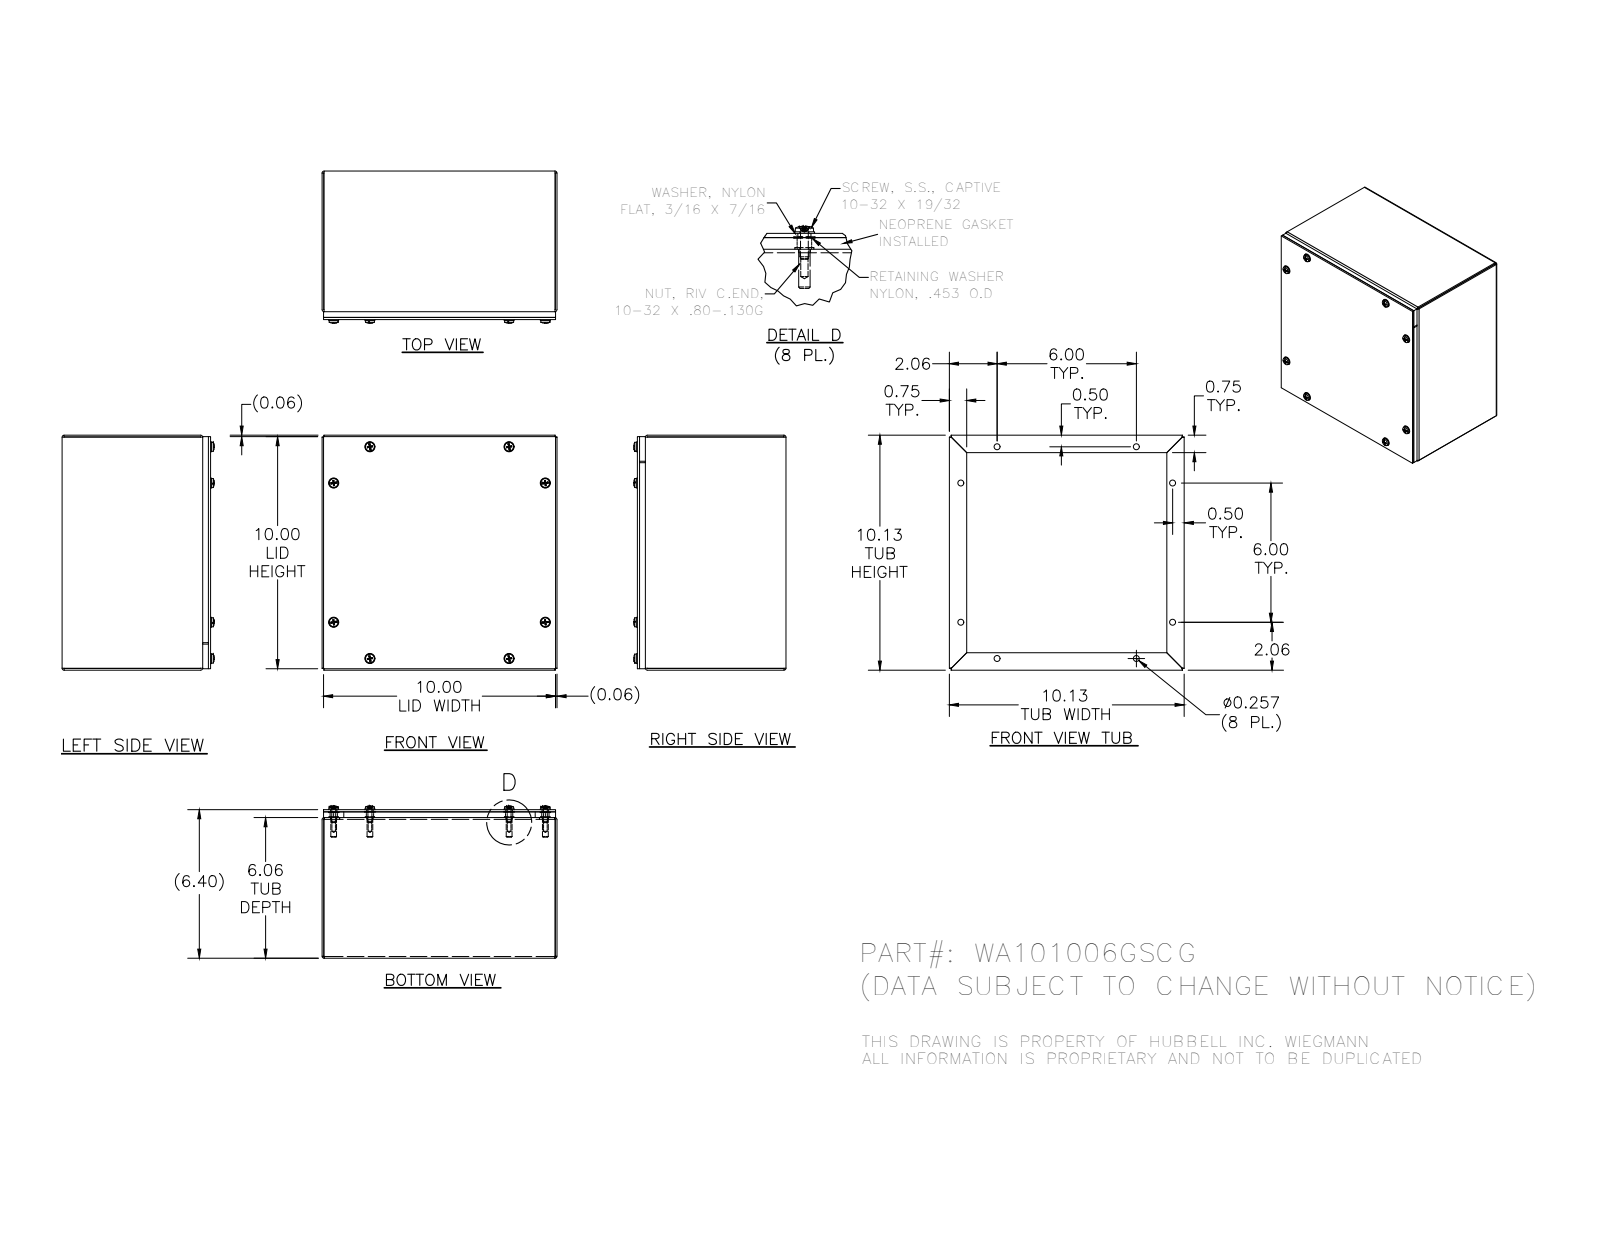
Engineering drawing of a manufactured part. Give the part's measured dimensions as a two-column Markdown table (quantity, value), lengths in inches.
| quantity | value |
| --- | --- |
| part name | 37210; WA101006GSCG; 316297; WA101006GSCGBKP (+4 more) |
| STEP written by | SolidWorks 2014 (AUTOMOTIVE_DESIGN) |
| units | inches |
| bodies | 36 solids, 892 faces (420 planar, 240 cylindrical, 232 other) |
| overall size | 10.125 × 10.125 × 6.558 |
| volume | 44.62 in³ |
| surface area | 1 044 in² |
| round holes (diameter × count) | 0.156 × 8, 0.188 × 8, 0.196 × 8, 0.257 × 8, 0.278 × 8, 0.281 × 8, 0.313 × 8 |
| round bosses / shafts (diameter × count) | 0.453 × 8, 0.437 × 8, 0.406 × 8, 0.248 × 8, 0.167 × 8 |
| partial cylindrical surfaces (radius × count) | 0.016 × 8, 0.089 × 8, 0.09 × 8 |
| main face-to-face distances | 0.074, 10.051, 10.125, 9.977, 0.094, 6.33, 6.404, 6.236, 6.31, 5.986 |
| hole center spacings | 6, 7.722, 7.722, 7.722, 10.694, 2.209, 10.921, 7.721 |
